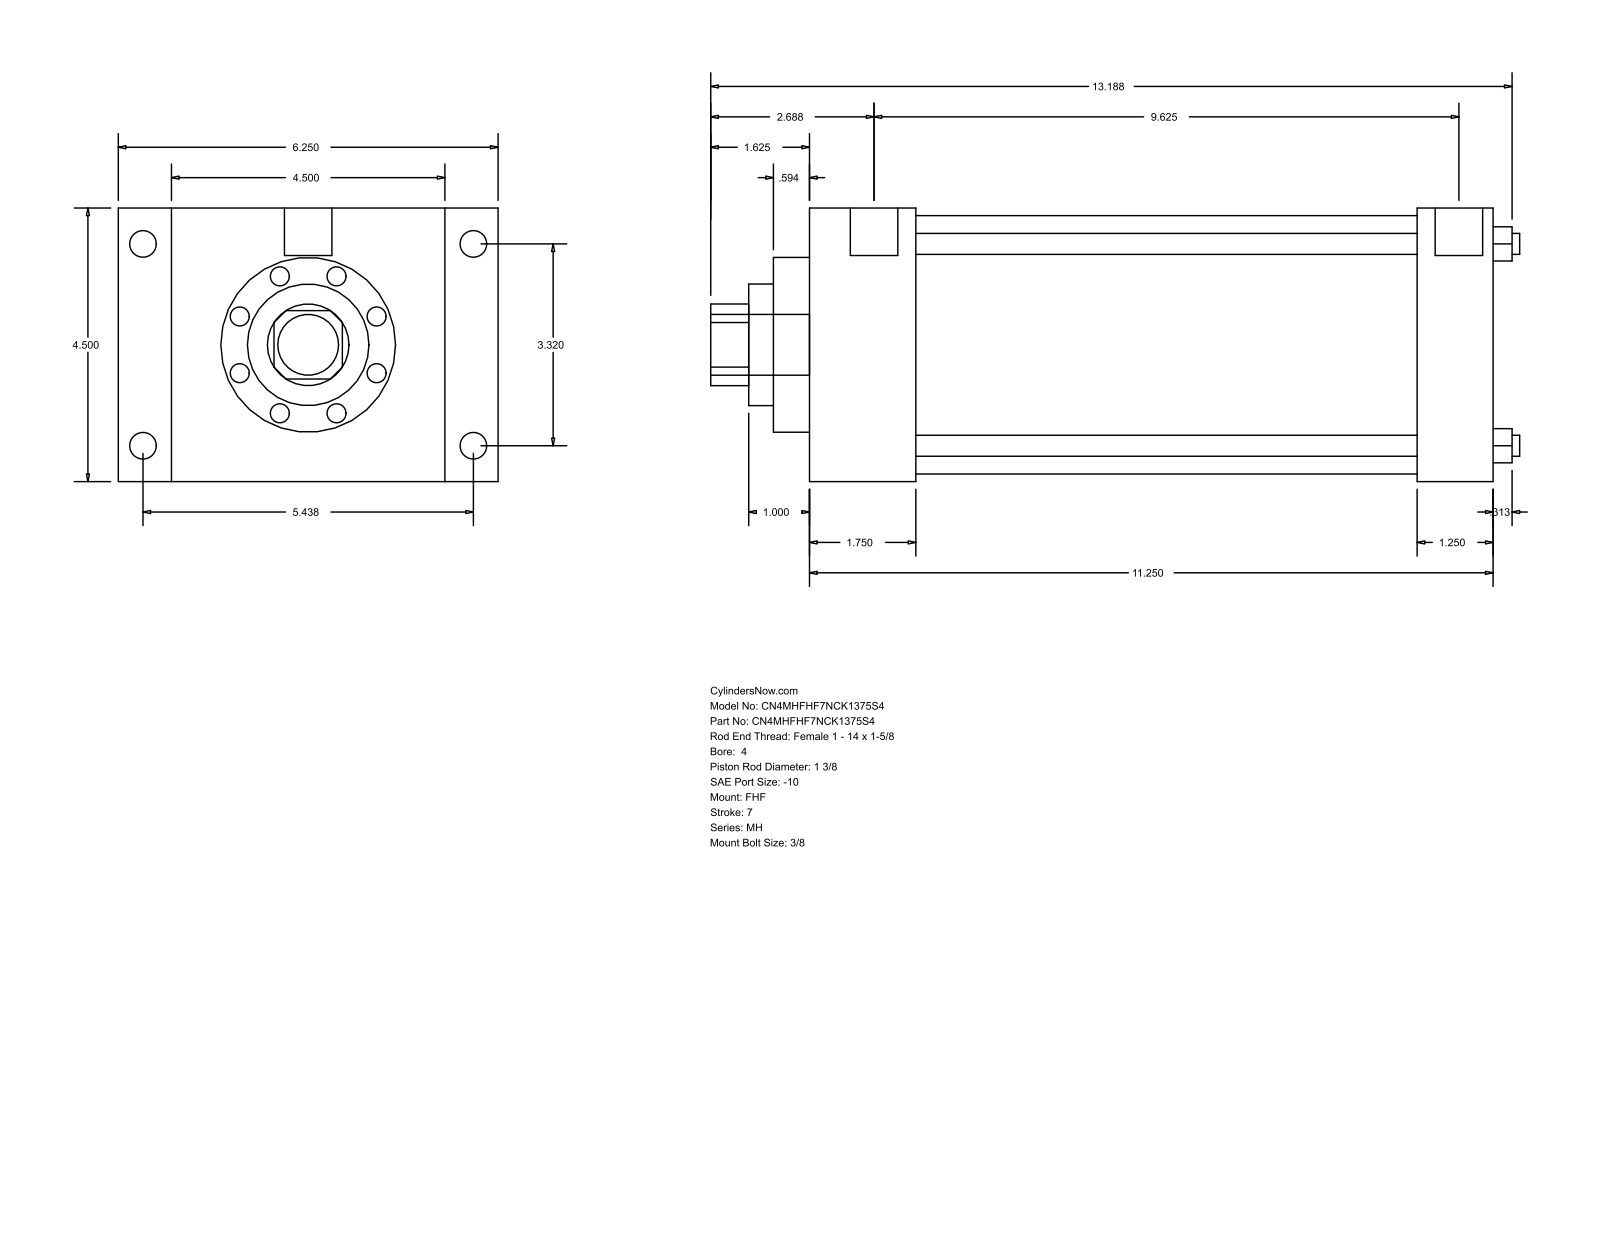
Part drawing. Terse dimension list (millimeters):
name: MH_FHF__0400_1.375
written by: GSSL Pune (CONFIG_CONTROL_DESIGN)
unit: mm
bodies: 0 solids, 90 faces (61 planar, 29 cylindrical, 0 other)
size: 338.14 × 158.75 × 114.3
holes: 4× ⌀8.76, 1× ⌀34.92, 1× ⌀50.8, 1× ⌀73.03, 1× ⌀107.95
bosses: 4× ⌀11.13, 4× ⌀8.73, 2× ⌀19.84, 1× ⌀25.4
rounds: 1× R17.06
face distances: 114.3, 285.75, 44.45, 241.3, 22.23, 136.53, 158.76, 254, 209.55, 31.75
hole spacings: 59.62, 84.32, 119.25
